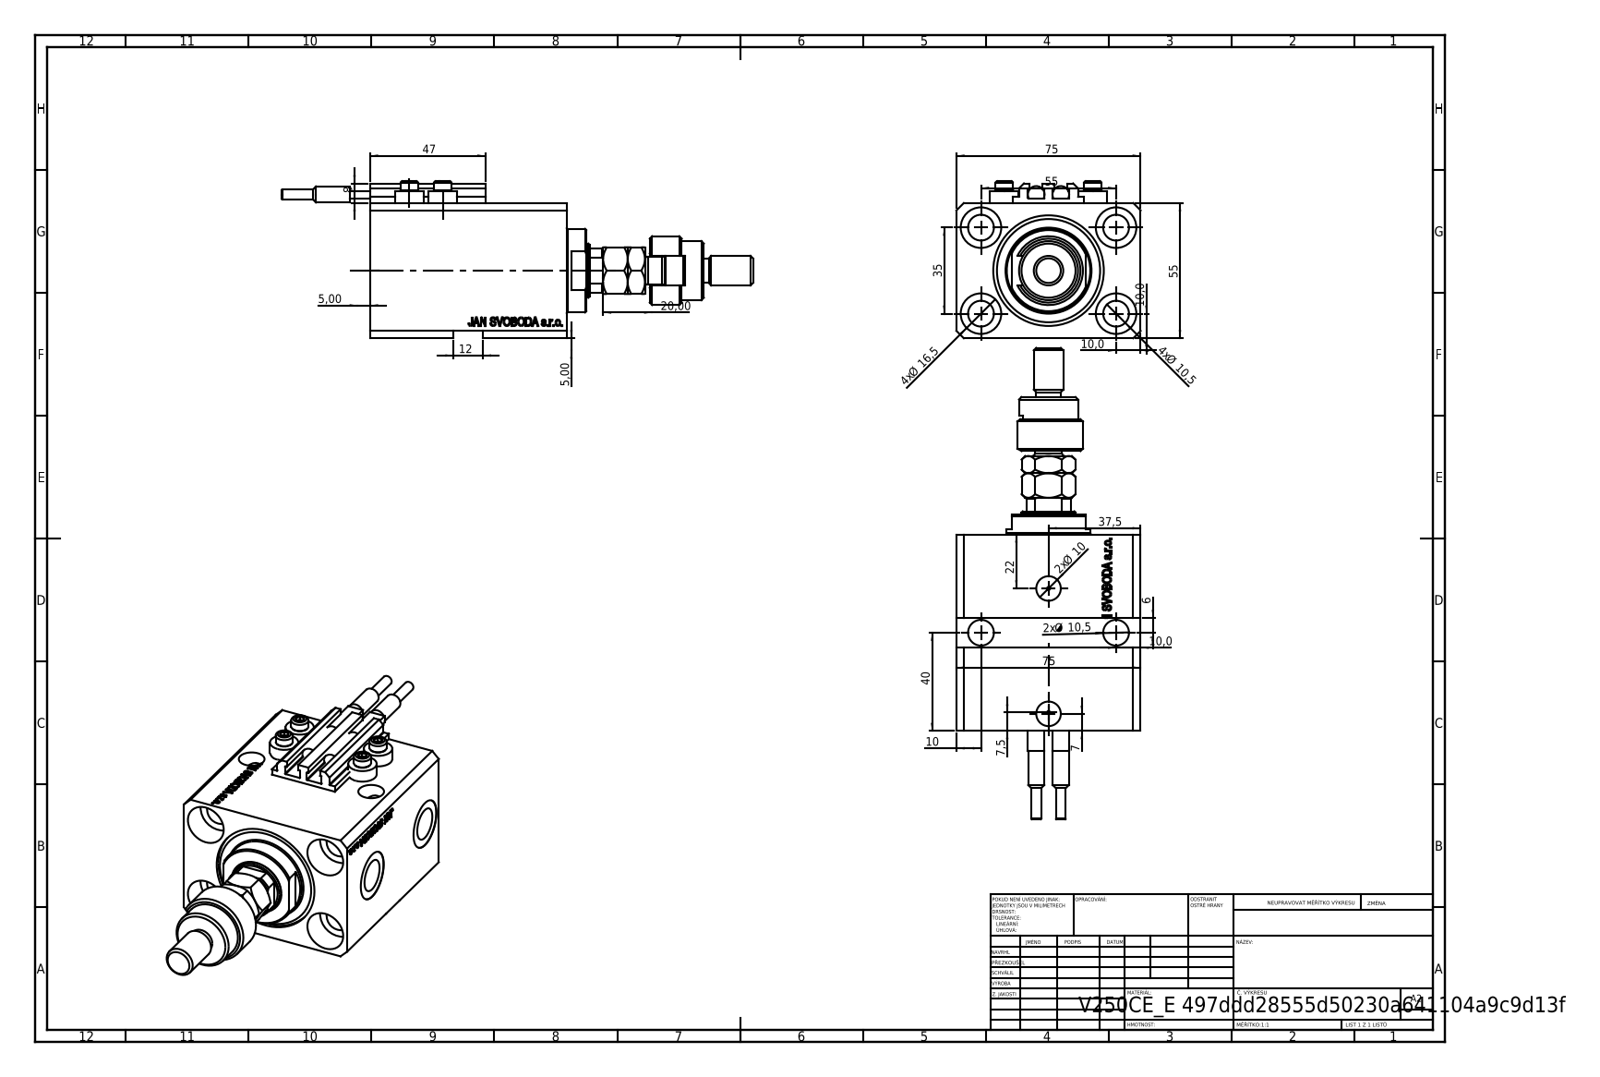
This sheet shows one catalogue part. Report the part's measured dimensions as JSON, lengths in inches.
{"part_name": "V250CE_VC_E; FEMALE_PART_FOR_DFA; MFA; SWITCH_V250CE (+3 more)", "step_written_by": "SolidWorks 2019 (CONFIG_CONTROL_DESIGN)", "units": "inches", "bodies": {"solids": 12, "faces": 1201, "planar": 574, "cylindrical": 151, "other": 476}, "overall_size": [7.555, 2.953, 2.52], "volume_in3": 18.63, "surface_area_in2": 134.8, "round_holes": [[0.413, 7], [0.049, 4], [0.157, 4], [0.65, 4], [0.394, 2], [0.518, 2], [0.787, 2], [0.866, 1], [1.26, 1], [1.772, 1]], "round_bosses_or_shafts": [[0.457, 4], [0.276, 4], [0.268, 2], [0.256, 2], [0.157, 2], [1.339, 1], [1.102, 1], [0.945, 1]], "partial_cylinders_radius": [[0.008, 10], [0.384, 1], [0.413, 1]], "face_to_face_distances": [2.165, 2.953, 0.118, 1.067, 3.15, 2.083, 0.39, 2.244, 1.693, 2.76], "hole_center_spacings": [1.283, 2.165, 0.535, 0.555, 0.783, 0.792, 1.016, 1.121]}
